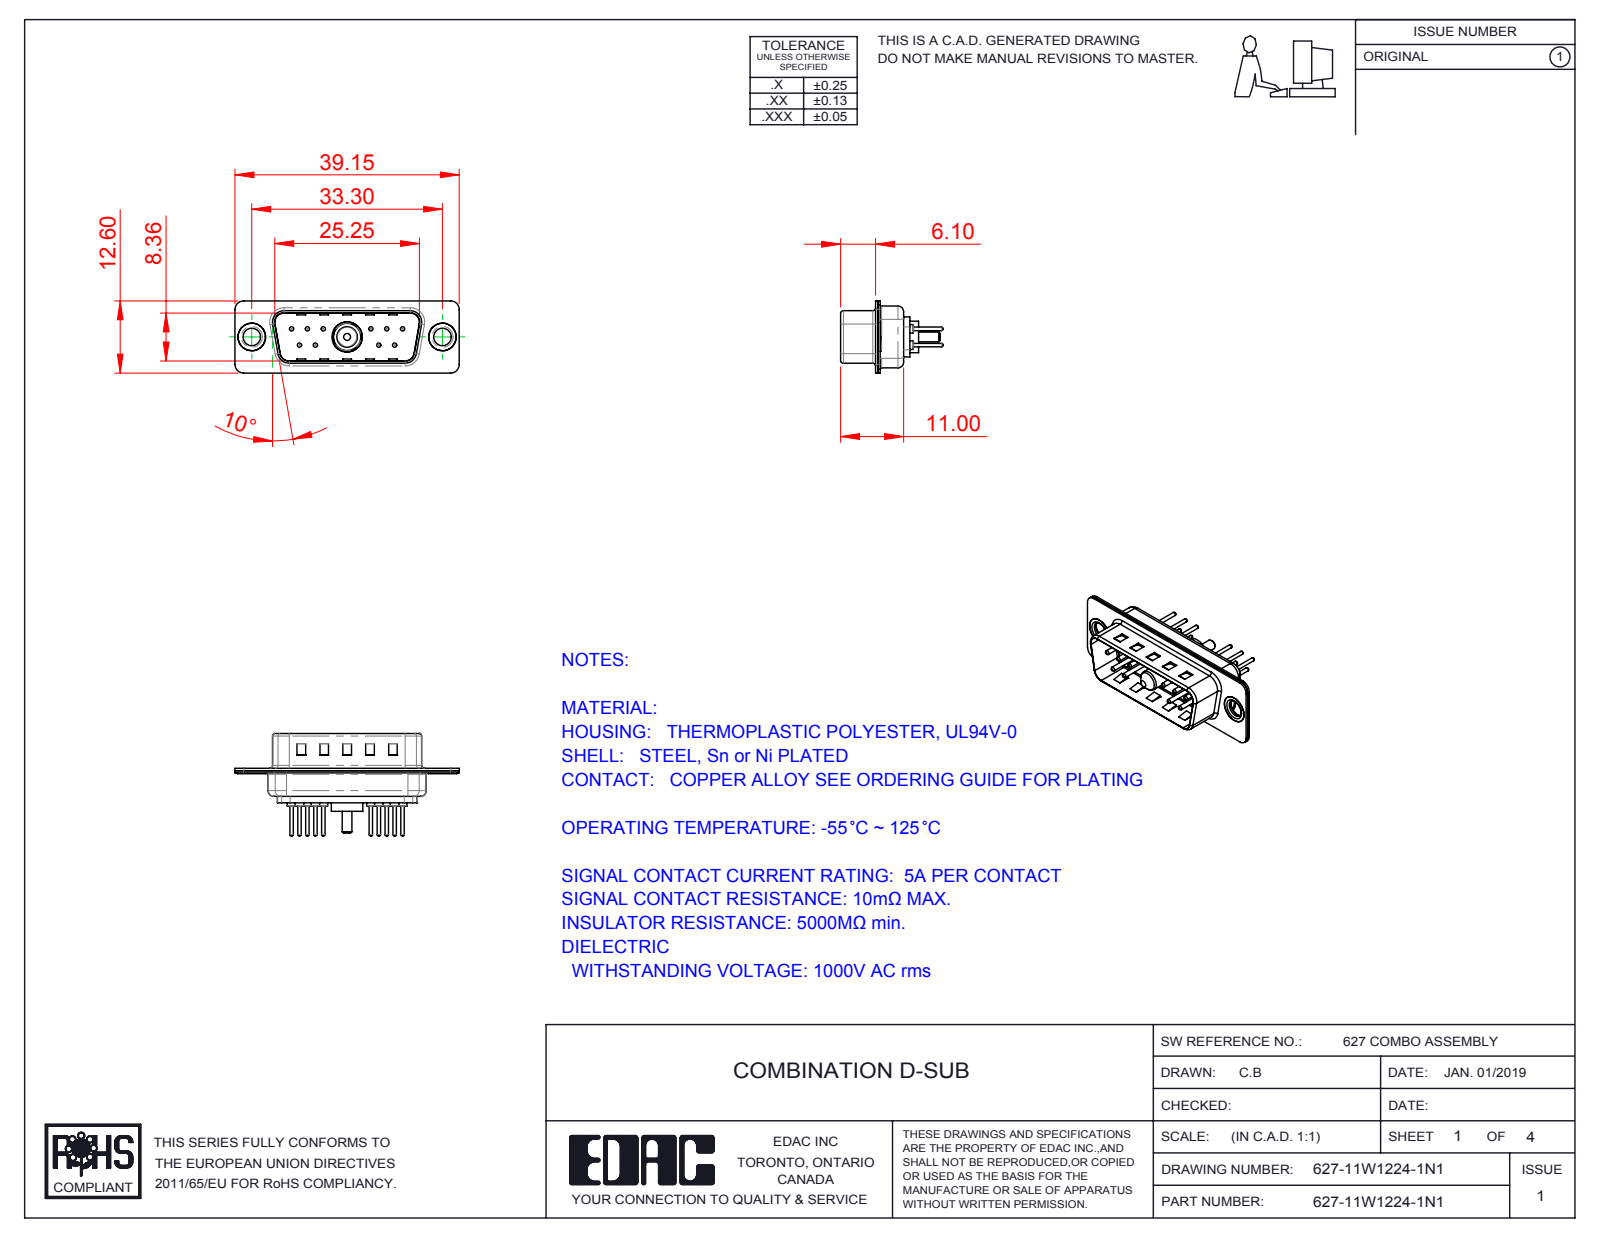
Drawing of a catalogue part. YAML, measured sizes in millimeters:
part_name: "627Combo Contact Row 2_24; 627Combo Housing_11W1; 627-11W1224-1N1; 627Combo Shell Rear_15 Contacts (+4 more)"
step_written_by: "SolidWorks 2016 (CONFIG_CONTROL_DESIGN)"
units: millimeters
bodies: {solids: 17, faces: 737, planar: 228, cylindrical: 280, other: 229}
overall_size: [39.15, 17.9, 12.6]
volume: 1819
surface_area: 4631
round_holes:
  - {diameter: 0.75, count: 10}
  - {diameter: 1.6, count: 10}
  - {diameter: 2, count: 10}
  - {diameter: 3.05, count: 2}
  - {diameter: 4, count: 2}
  - {diameter: 4.8, count: 2}
  - {diameter: 4.85, count: 1}
  - {diameter: 5.3, count: 1}
round_bosses_or_shafts:
  - {diameter: 1.5, count: 10}
  - {diameter: 0.6, count: 10}
  - {diameter: 5, count: 2}
  - {diameter: 4.9, count: 2}
  - {diameter: 3.55, count: 2}
  - {diameter: 5.5, count: 1}
  - {diameter: 5.2, count: 1}
  - {diameter: 4.75, count: 1}
partial_cylinders:
  - {radius: 1.5, count: 20}
  - {radius: 2, count: 12}
  - {radius: 0.5, count: 8}
  - {radius: 1.6, count: 8}
  - {radius: 1, count: 7}
  - {radius: 0.25, count: 4}
  - {radius: 0.6, count: 4}
  - {radius: 0.65, count: 4}
face_to_face_distances: [0.4, 0.82, 9.58, 0.8, 8.76, 1.5, 5.6, 5.2, 6, 1.22]
hole_center_spacings: [3.16, 2.77, 13.85, 11.08, 16.62, 5.03, 5.04, 5.54]
